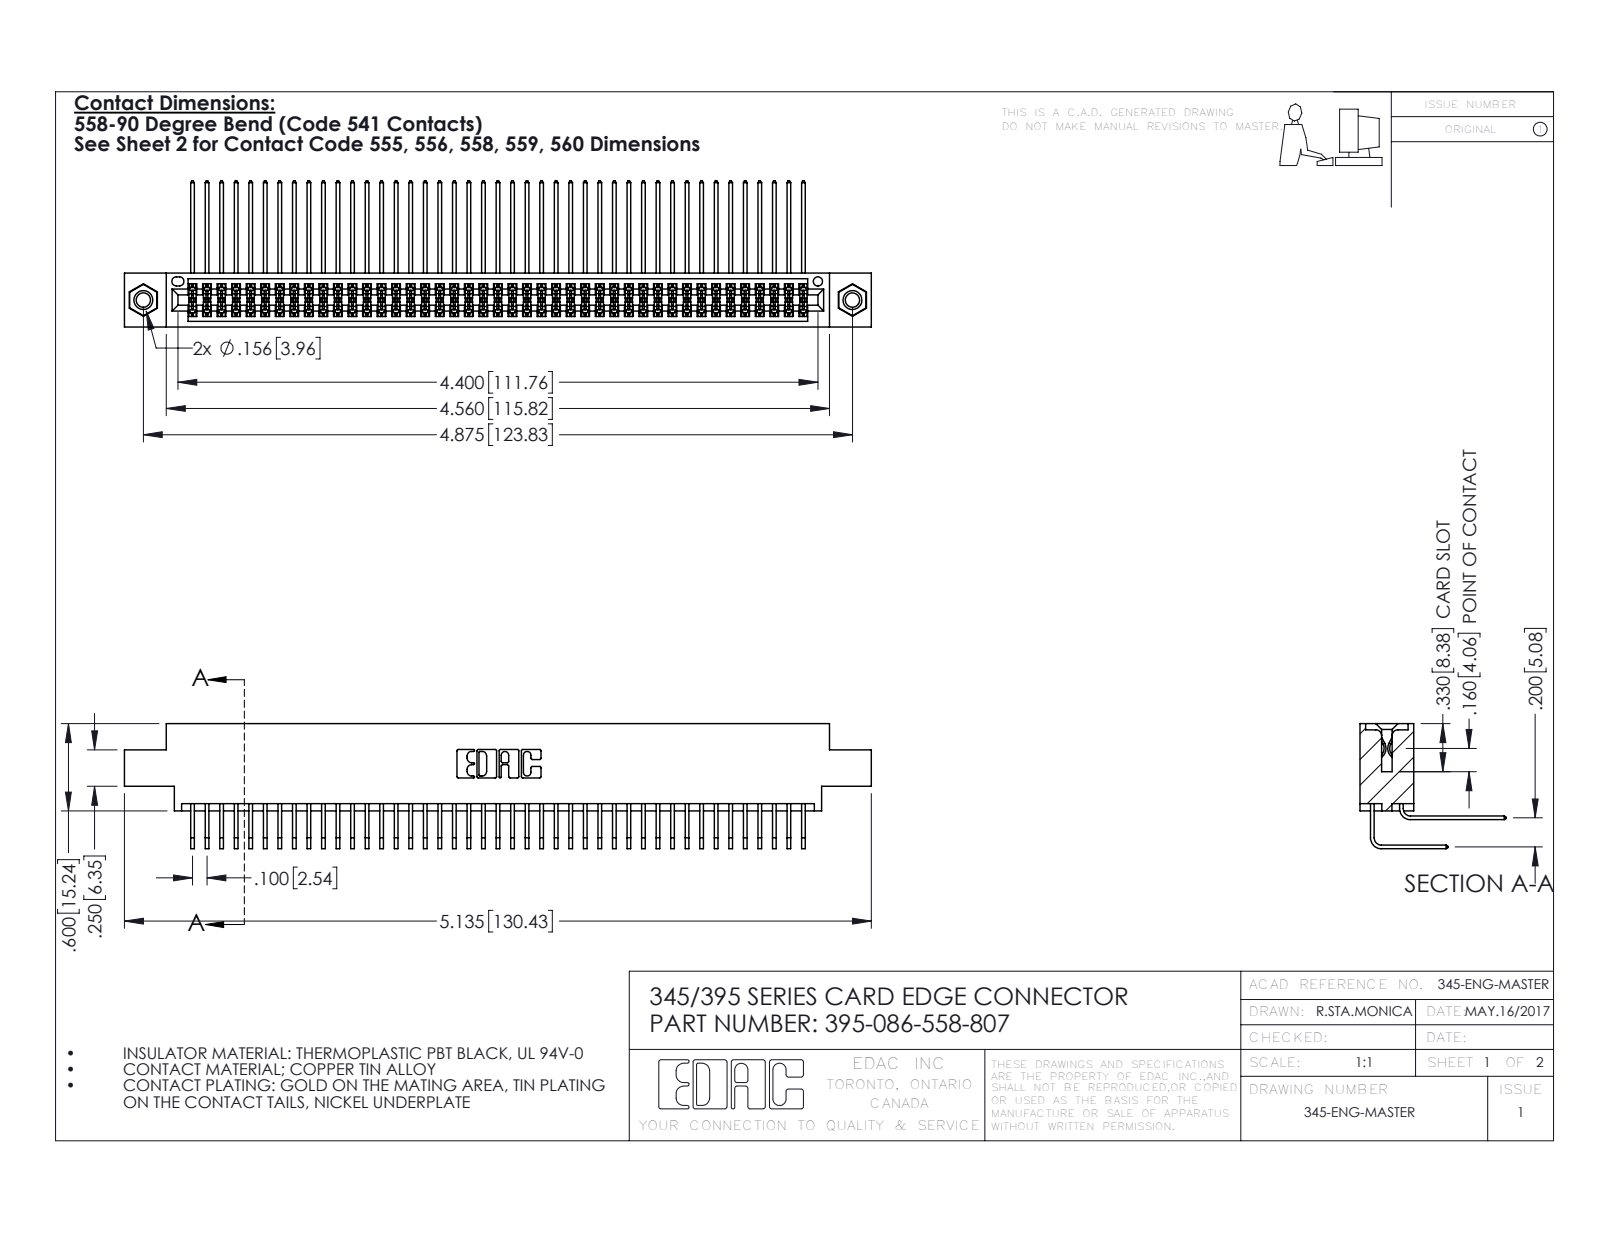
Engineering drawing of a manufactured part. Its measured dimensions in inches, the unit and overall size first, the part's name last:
Units: inches
Overall size (bounding box): 5.135 × 1.005 × 0.859
Round holes (diameter × count): ⌀0.098 ×2, ⌀0.125 ×2, ⌀0.156 ×2, ⌀0.064 ×1
Round bosses / shafts (diameter × count): ⌀0.155 ×2
Partial cylindrical surfaces — rounded edges, fillets, slot ends (radius × count): R0.006 ×130, R0.01 ×22, R0.007 ×6, R0.031 ×6, R0.026 ×3, R0.014 ×2, R0.019 ×2, R0.022 ×2
Main face-to-face distances: 0.072, 0.298, 0.2, 0.37, 0.098, 0.272, 0.025, 0.225, 0.175, 0.025
Hole centre spacings: 0.27, 4.639, 4.875
Volume: 0.796 in³ · Surface area: 33.81 in²
Bodies: 89 solids, 4662 faces (3126 planar, 1520 cylindrical, 16 other)
Part name (STEP PRODUCT): 395-086-558-807; 345-250-001_345-250-005-103; 345-292-001_558 559 Tail - 1; 345-292-001_558 Tail - 2 (+1 more)
STEP written by: SolidWorks 2016 (CONFIG_CONTROL_DESIGN)
